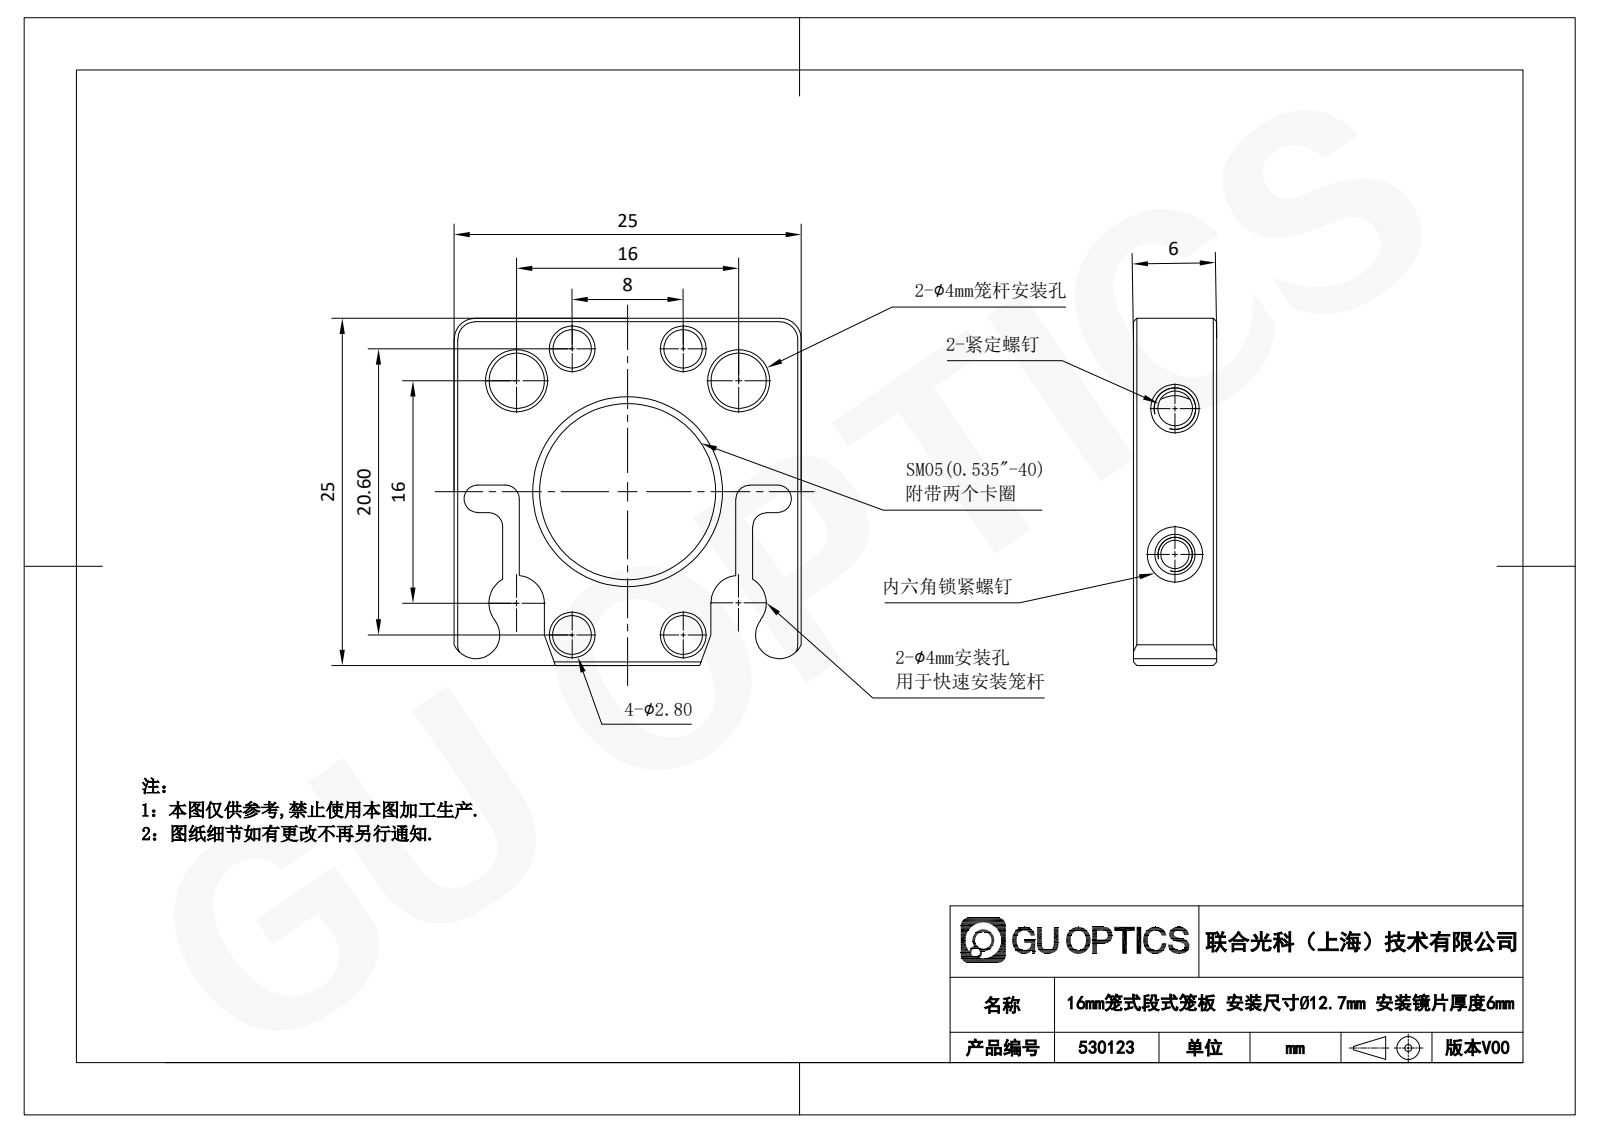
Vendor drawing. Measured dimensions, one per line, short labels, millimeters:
name: 530123
written by: SolidWorks 2020 (CONFIG_CONTROL_DESIGN)
unit: mm
bodies: 4 solids, 137 faces (55 planar, 34 cylindrical, 48 other)
size: 25 × 25 × 6
volume: 2 266 mm³; area: 2 813 mm²
holes: 4× ⌀2.8, 2× ⌀4, 1× ⌀2.05, 1× ⌀2.5, 1× ⌀2.9, 1× ⌀4.8, 1× ⌀11, 1× ⌀12.7
bosses: 1× ⌀13.59, 1× ⌀3
rounds: 6× R1, 2× R1.5, 2× R1.72, 2× R2
face distances: 6, 25, 2, 4, 4.7, 20.3, 1.2, 12, 3.5, 21.5
hole spacings: 11.05, 4.61, 8, 11.31, 12.22, 18.73, 20.6, 21.88
